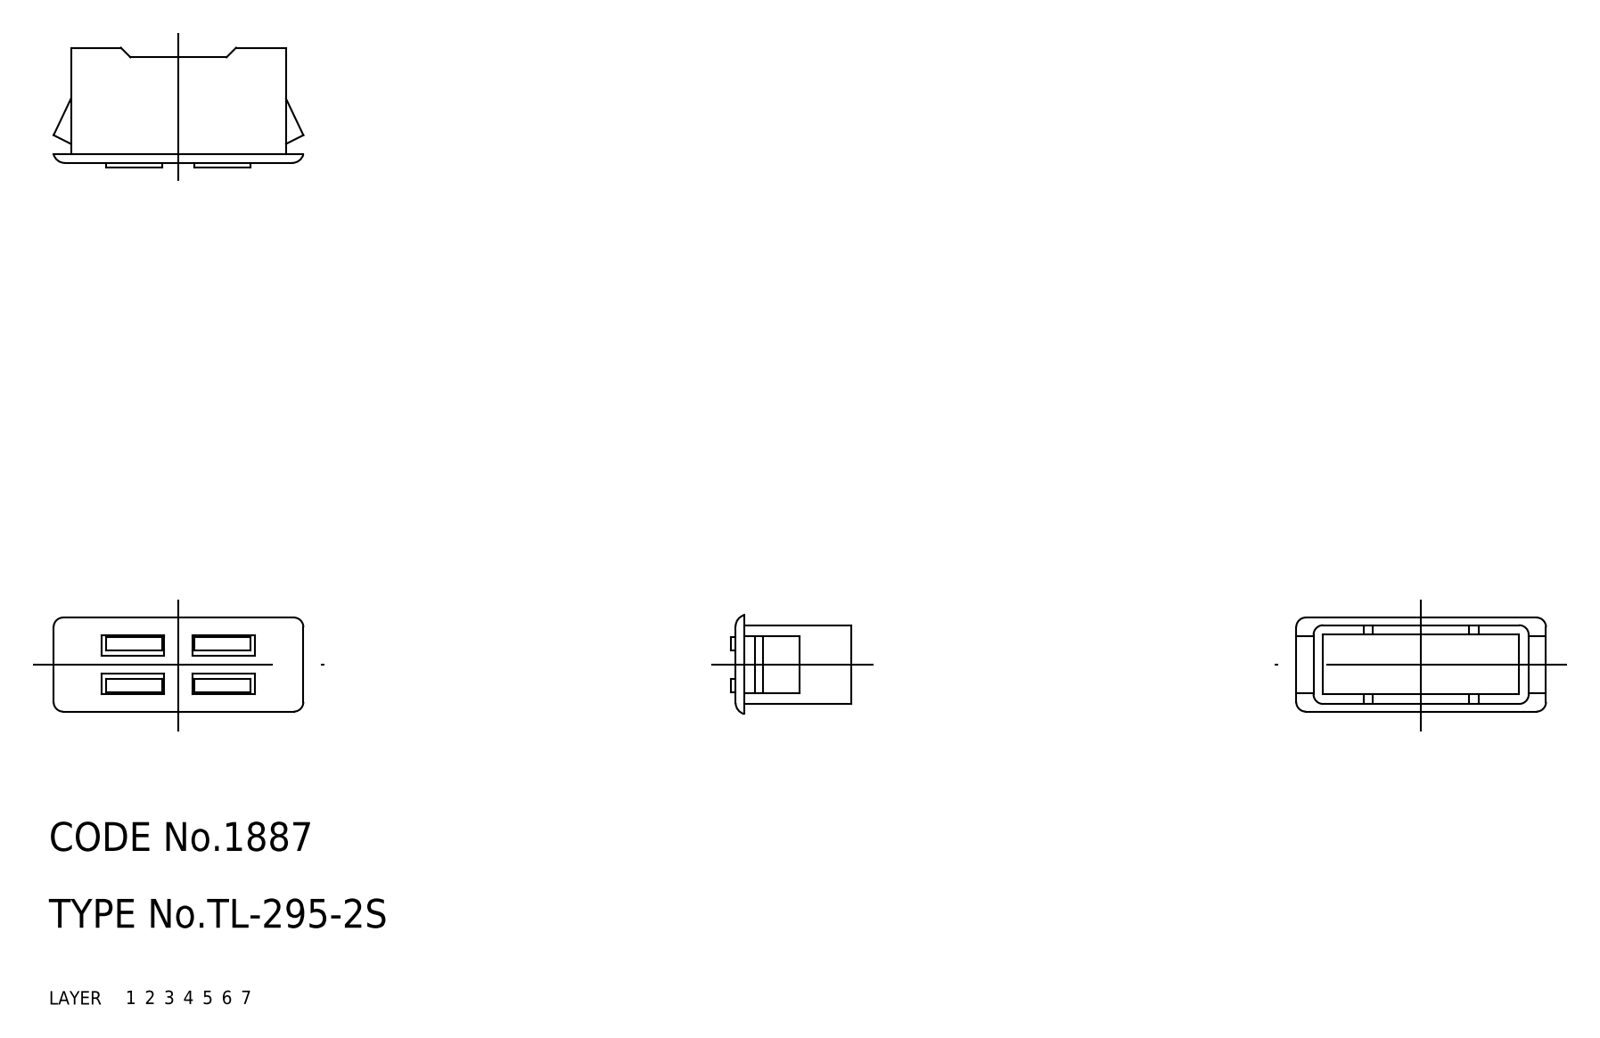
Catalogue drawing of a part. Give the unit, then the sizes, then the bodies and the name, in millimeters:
Units: millimetres
Overall size (bounding box): 26 × 12.5 × 9.8
Volume: 1 741 mm³ · Surface area: 3 106 mm²
Bodies: 4 solids, 87 faces (0 planar, 0 cylindrical, 87 other)
Part name (STEP PRODUCT): attachment; spring; housing; TL_295_2S_6750_36
STEP written by: CADfix (AUTOMOTIVE_DESIGN)
